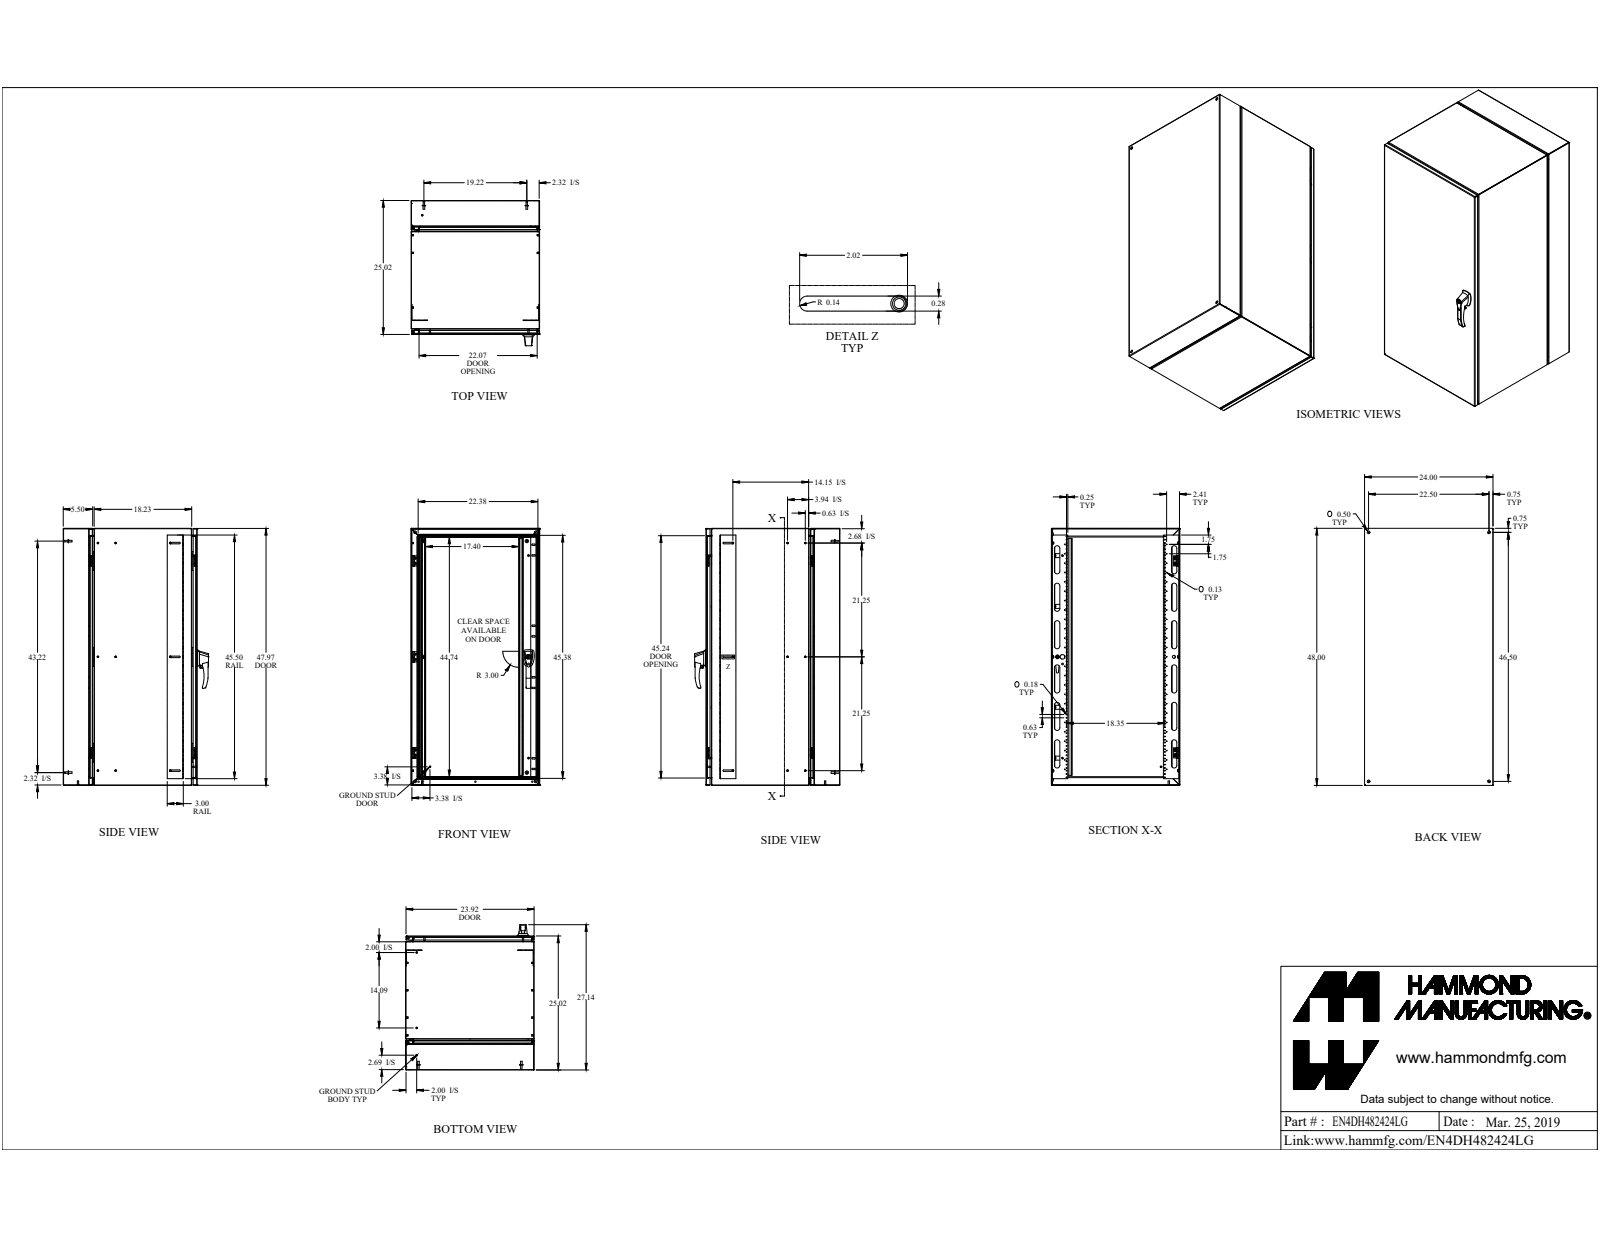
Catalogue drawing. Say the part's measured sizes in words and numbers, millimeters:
The part is named "EN4DH482424LG". Its 3-D file was written by "SolidWorks 2019 (CONFIG_CONTROL_DESIGN)". It is 240 solids with 4902 faces: 2608 planar, 1359 cylindrical and 935 other. Overall it measures 1219.2 by 689.2 by 609.6 millimeters. Its volume is 10 120 000 cubic millimeters and its surface area 10 550 000 square millimeters. Round holes: 156 of diameter 4.5, 50 of diameter 3.2, 23 of diameter 6.4, 19 of diameter 5, 14 of diameter 4.8, 14 of diameter 4.9, 14 of diameter 6, 9 of diameter 6.5, 9 of diameter 7, 8 of diameter 7, 7 of diameter 6.7, 6 of diameter 7.1. Round bosses or shafts: 30 of diameter 6.4, 18 of diameter 8, 16 of diameter 6, 14 of diameter 12, 14 of diameter 11, 14 of diameter 4.7, 11 of diameter 15.9, 8 of diameter 15.9. Partial cylindrical surfaces (rounded edges, fillets, slot ends): 37 of radius 0.9, 37 of radius 2.7, 26 of radius 6.4, 25 of radius 3.2, 25 of radius 12.7, 24 of radius 1.5, 20 of radius 3.1, 19 of radius 3.3. The main face-to-face distances are 1.8, 633.7, 607.8, 605.9, 631.9, 635.5, 609.6, 1217.4, 2.4, 1.8. The hole center spacings are 25, 454.8, 454.8, 539.8, 639.8, 343.5, 454.8, 558.4.
